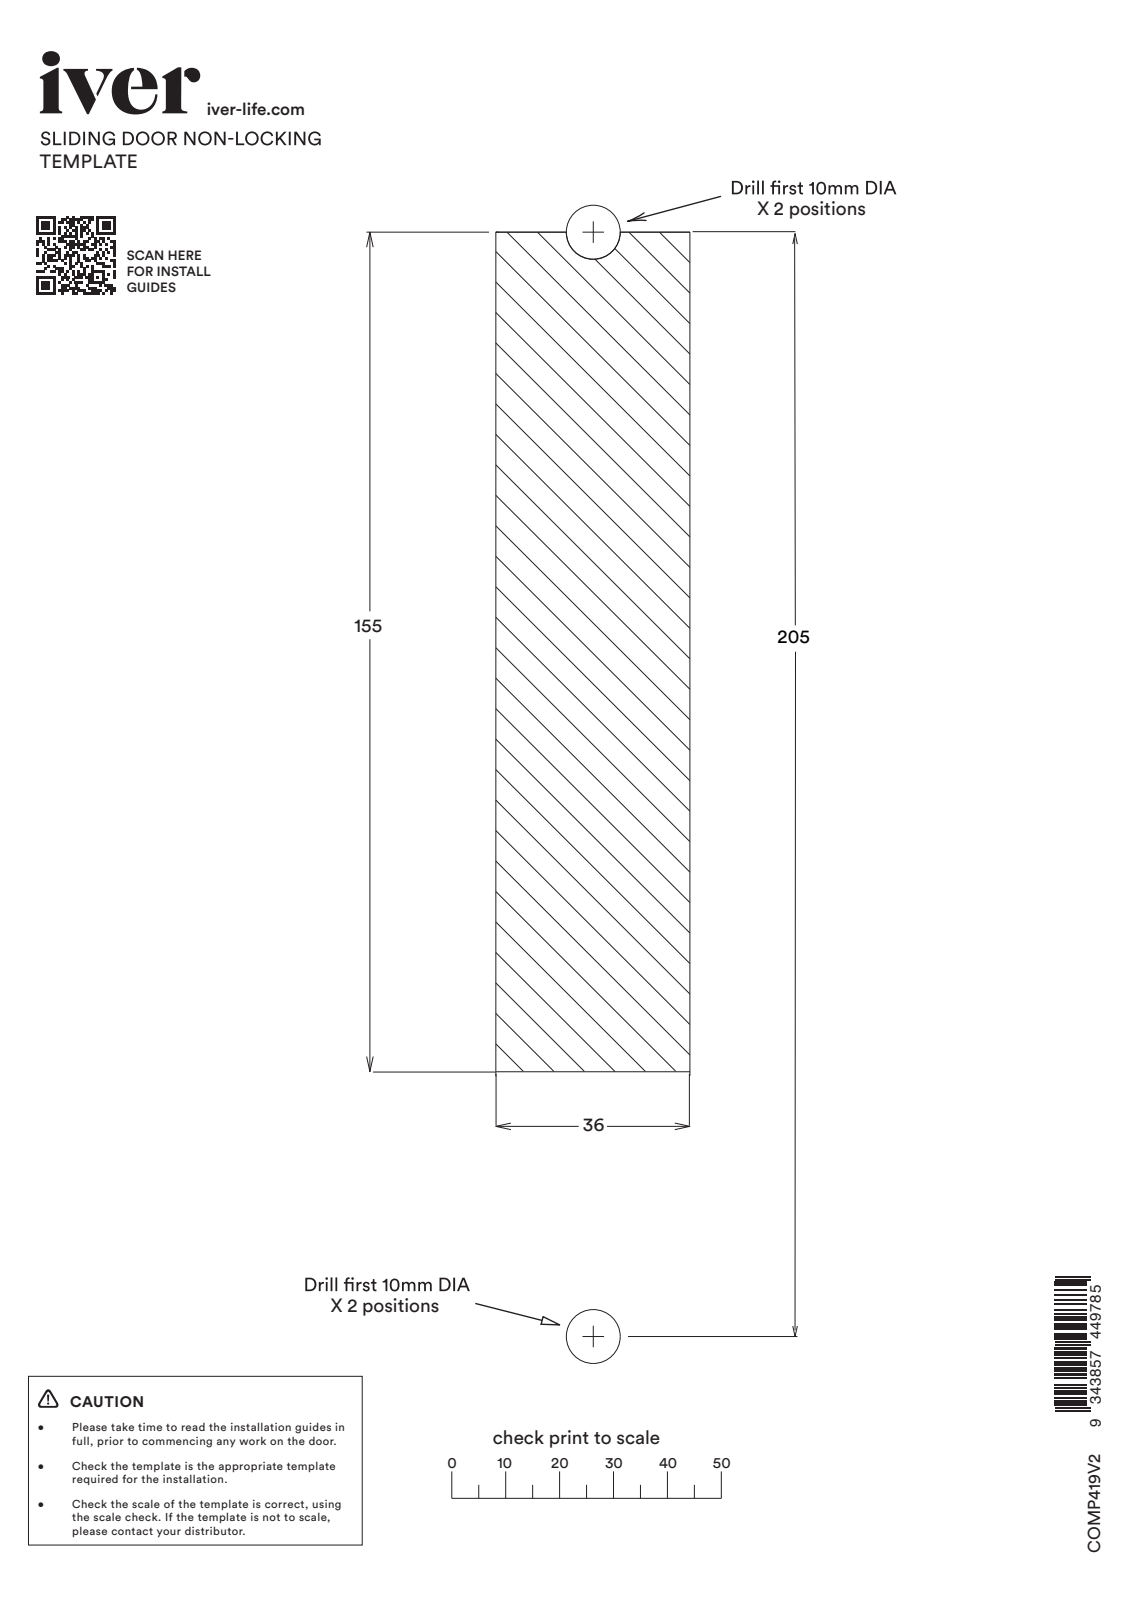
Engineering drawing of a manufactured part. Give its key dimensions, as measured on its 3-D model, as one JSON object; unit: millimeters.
{"part_name": "Lever 01 DDA; YSG Lever DDA; Lever DDA Bronze End Cap; BooleanFragments (+8 more)", "step_written_by": "FreeCAD (AUTOMOTIVE_DESIGN)", "units": "millimeters", "bodies": {"solids": 27, "faces": 1393, "planar": 588, "cylindrical": 424, "other": 381}, "overall_size": [223, 182.1, 60], "volume_mm3": 293619, "surface_area_mm2": 116746, "round_holes": [[3, 6], [1.7, 4], [5.8, 4], [4.5, 3], [6, 3], [9.5, 3], [1.5, 2], [4.22, 2], [4.9, 2], [5, 2], [2.5, 1], [14, 1]], "round_bosses_or_shafts": [[5.3, 3], [9.2, 2], [5, 2], [3, 2], [60, 1], [49.3, 1], [48.53, 1], [34.6, 1]], "partial_cylinders_radius": [[5, 33], [1, 16], [1.7, 8], [4.97, 8], [0.5, 4], [3, 4], [3.1, 4], [9.79, 4]], "face_to_face_distances": [5.2, 3, 11, 19, 213.21, 6.8, 189.8, 7.1, 190.1, 3.5], "hole_center_spacings": [9.51, 11.88, 20.34, 20.75, 25.06, 29.34, 30.01, 5.16]}
